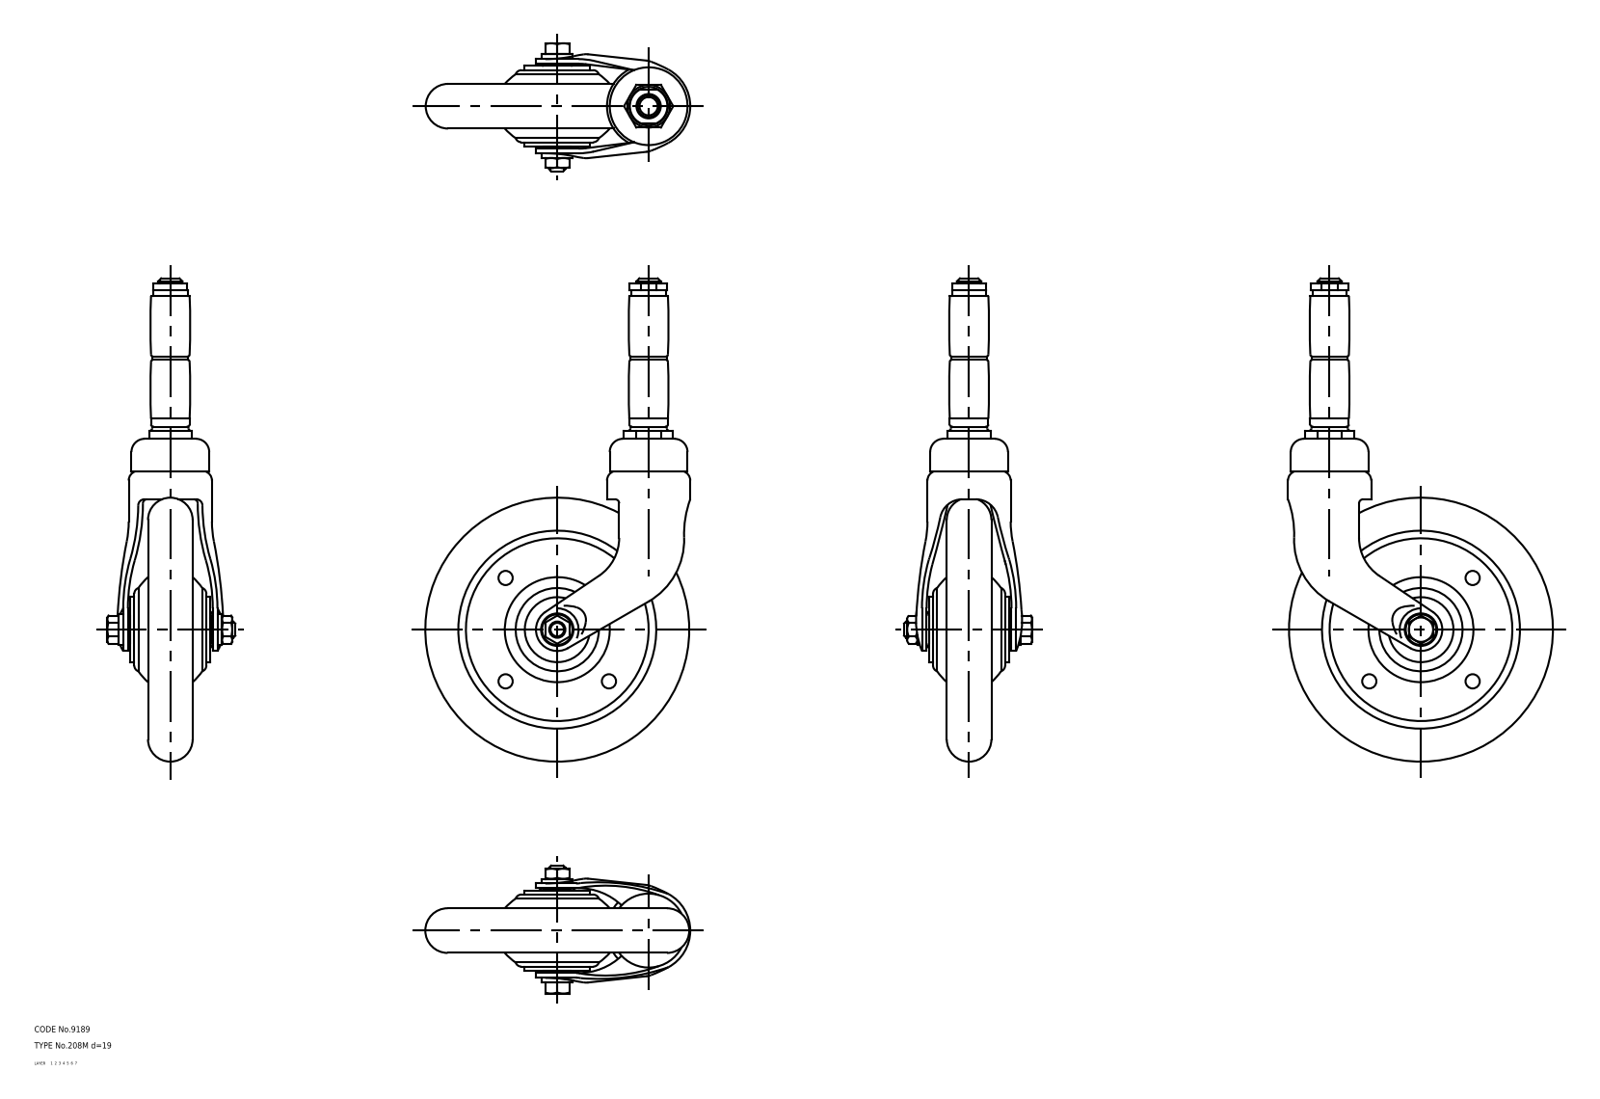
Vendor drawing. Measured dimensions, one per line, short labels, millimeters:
name: wheel; main shaft; axle; No_208M_d19_22215_36
written by: CADfix (AUTOMOTIVE_DESIGN)
unit: mm
bodies: 4 solids, 313 faces (0 planar, 0 cylindrical, 313 other)
size: 238 × 130.76 × 63
volume: 294 966 mm³; area: 70 082 mm²
